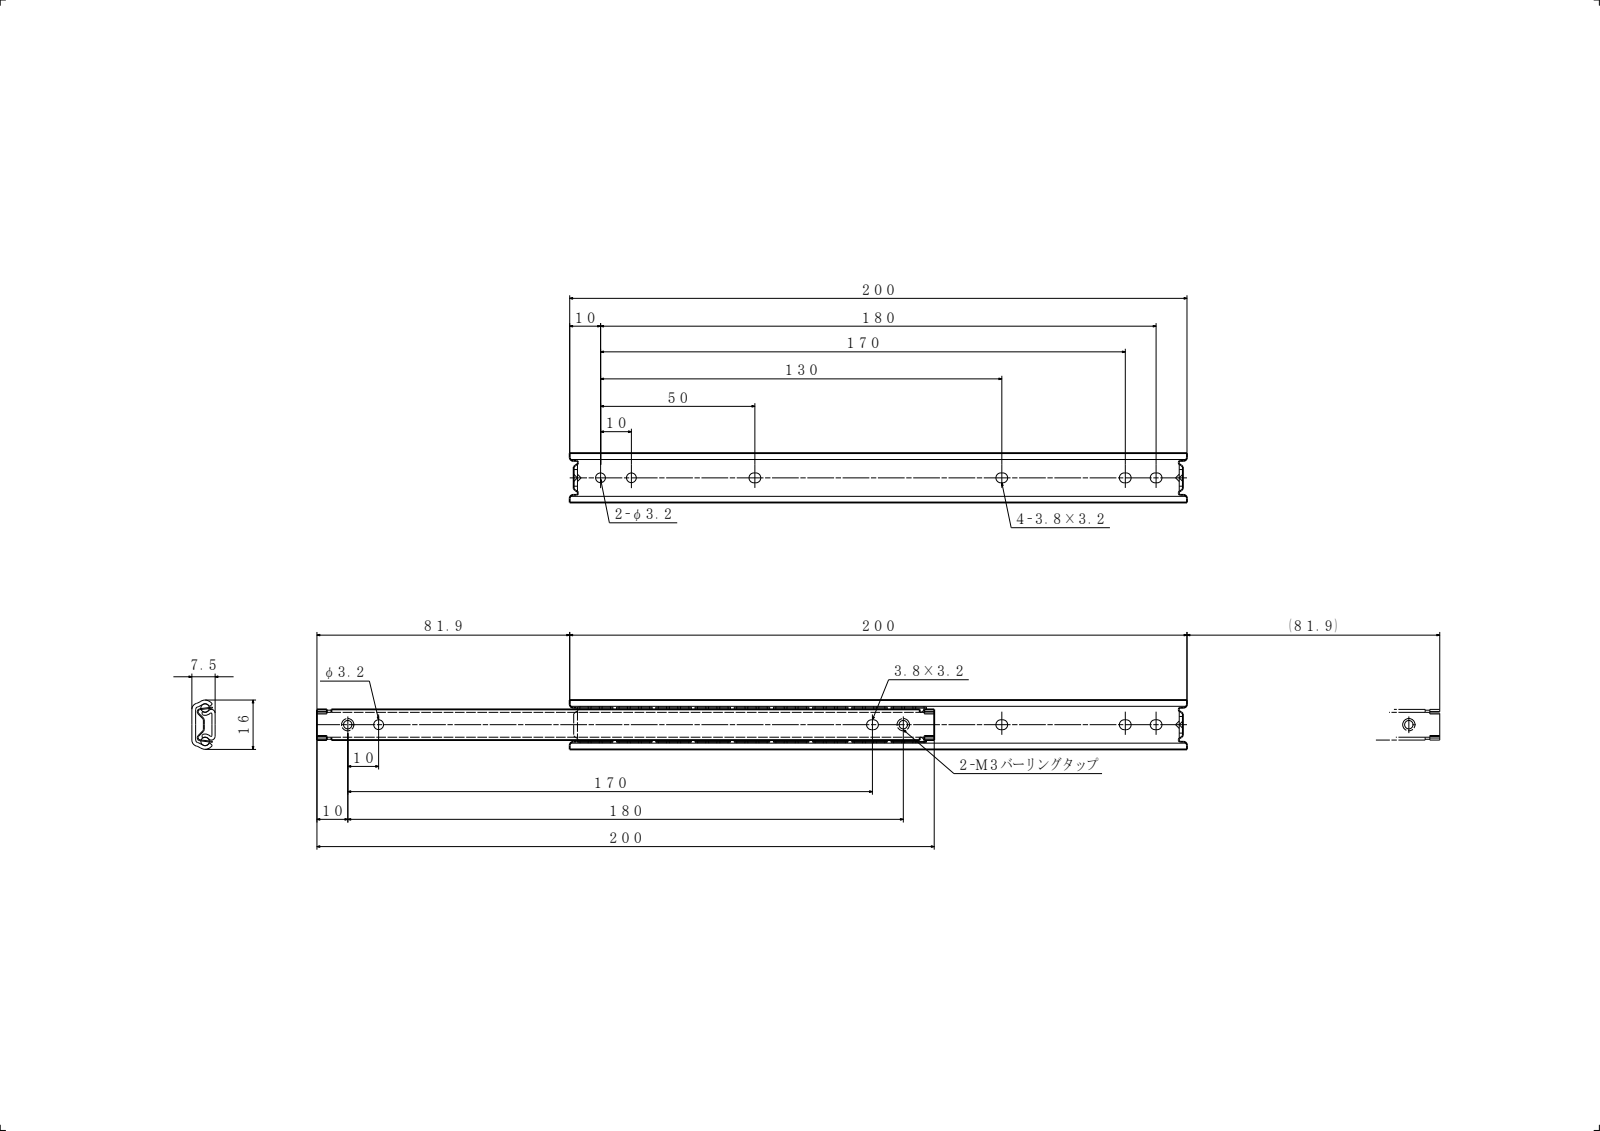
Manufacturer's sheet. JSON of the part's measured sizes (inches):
{"part_name": "U1620-200 IM; U1620-200; U1620-200 OM", "step_written_by": "SolidWorks 2019 (CONFIG_CONTROL_DESIGN)", "units": "inches", "bodies": {"solids": 2, "faces": 197, "planar": 80, "cylindrical": 99, "other": 18}, "overall_size": [11.098, 0.63, 0.295], "volume_in3": 0.545, "surface_area_in2": 26.47, "round_holes": [[0.126, 3], [0.11, 2]], "round_bosses_or_shafts": [[0.15, 2]], "partial_cylinders_radius": [[0.02, 22], [0.063, 10], [0.039, 6], [0.047, 6], [0.118, 4], [0.008, 2], [0.031, 2], [0.048, 2]], "face_to_face_distances": [0.047, 0.295, 0.248, 0.039, 0.256, 0.209, 0.375, 0.328, 7.724, 7.874], "hole_center_spacings": [0.394, 3.224, 2.831, 3.469, 3.618, 3.862, 6.693, 7.087]}
